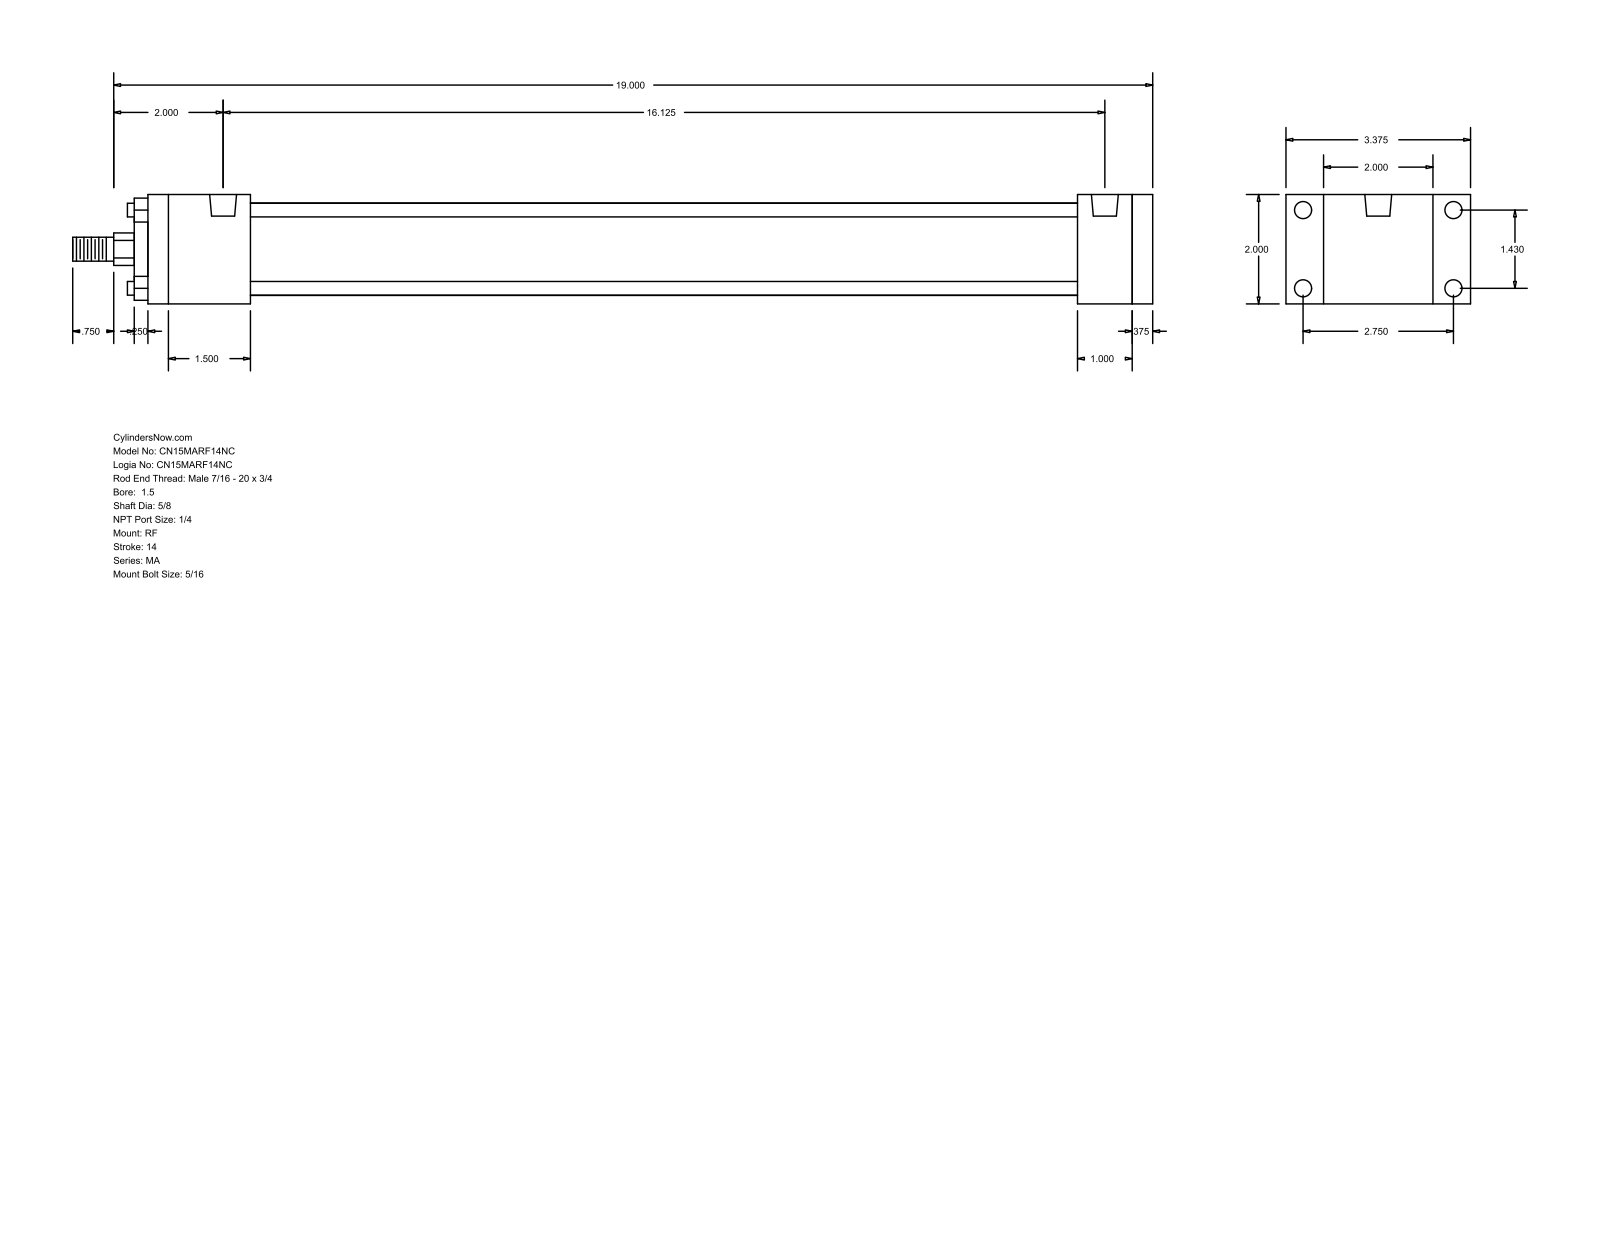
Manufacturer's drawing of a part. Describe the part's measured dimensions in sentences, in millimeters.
The part is named "MA_RF__0150_0.625". Its 3-D file was written by "GSSL Pune (CONFIG_CONTROL_DESIGN)". It is 0 solids with 92 faces: 64 planar, 28 cylindrical and 0 other. Overall it measures 501.65 by 85.72 by 50.8 millimeters. Round holes: 8 of diameter 7.94, 2 of diameter 12.49. Round bosses or shafts: 4 of diameter 6.35, 1 of diameter 42.93, 1 of diameter 28.57, 1 of diameter 15.88, 1 of diameter 11.11. Partial cylindrical surfaces (rounded edges, fillets, slot ends): 1 of radius 7.54. The main face-to-face distances are 50.8, 9.53, 466.72, 457.19, 431.8, 25.39, 34.92, 47.62, 384.18, 409.57. The hole center spacings are 36.32, 69.84, 78.72, 409.58.
